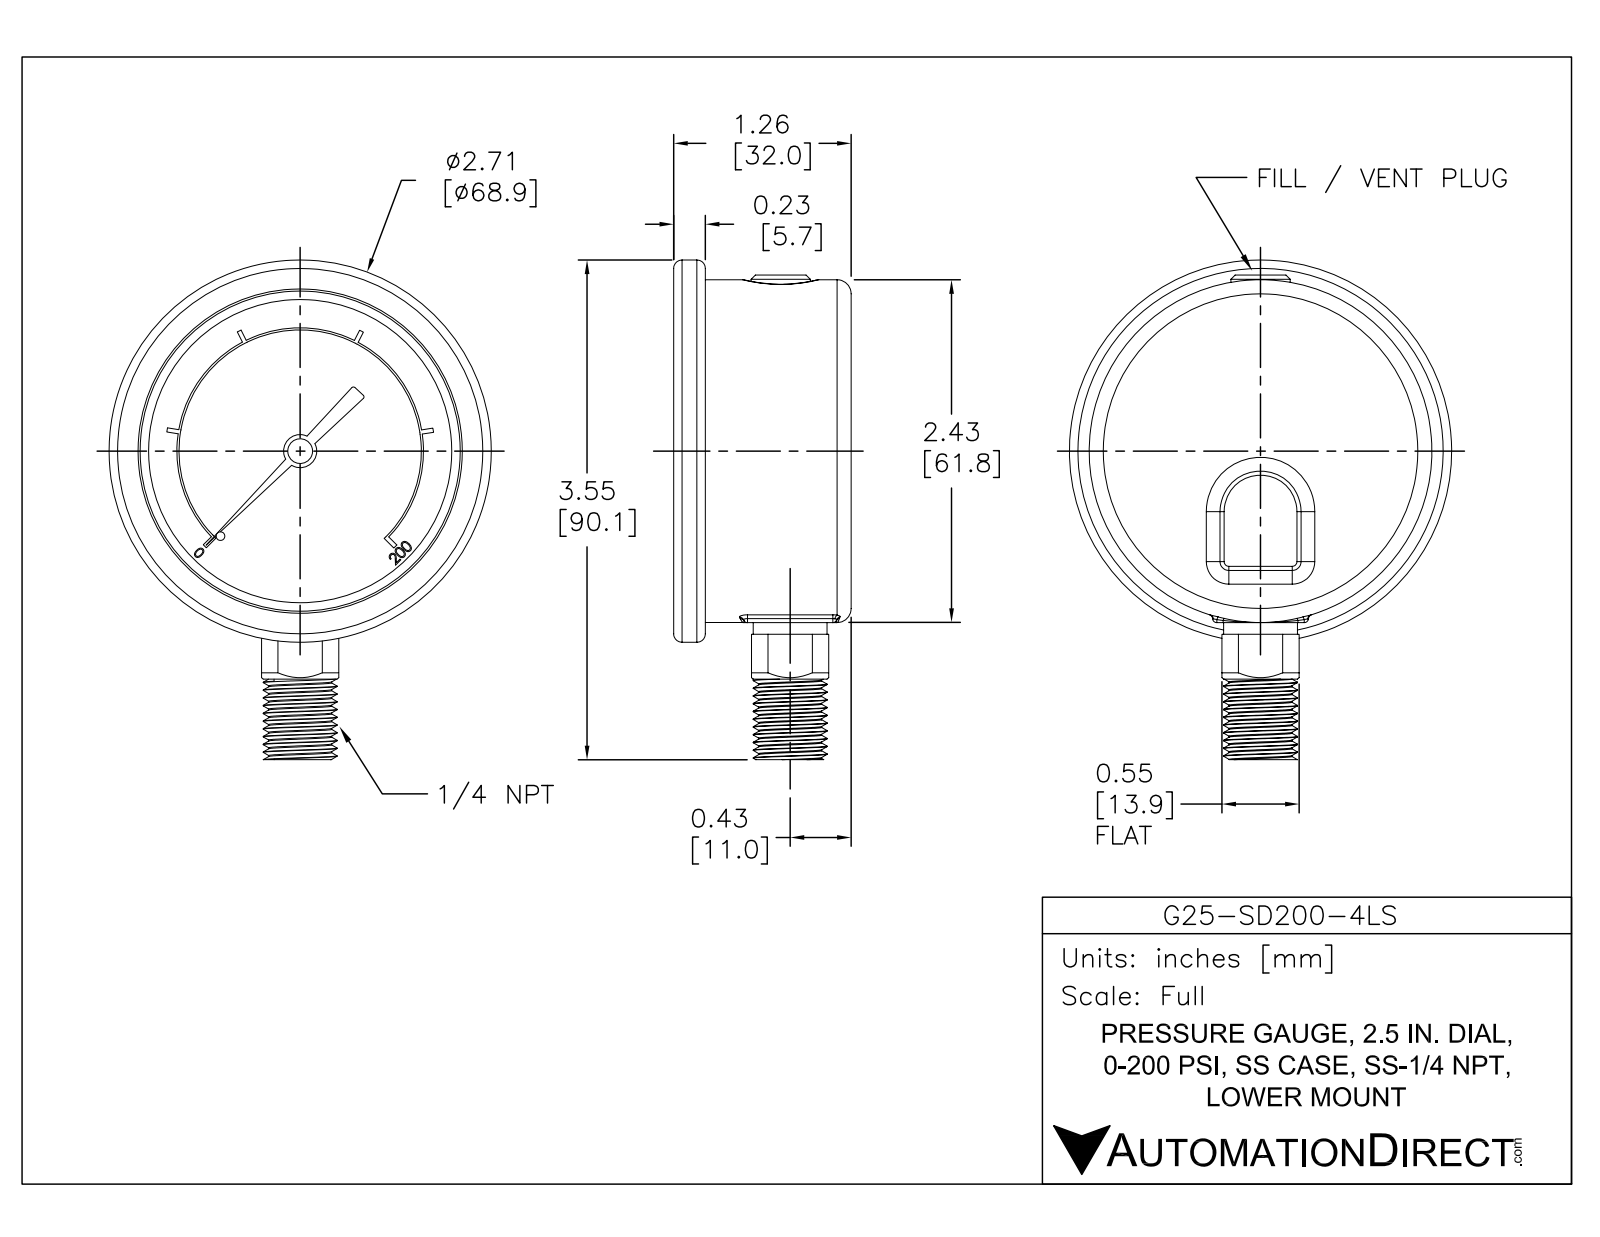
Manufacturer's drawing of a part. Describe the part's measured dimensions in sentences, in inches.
The part is named "G25-SD200-4LS". Its 3-D file was written by "SolidWorks 2021 (AUTOMOTIVE_DESIGN)". It is 1 solid with 349 faces: 195 planar, 85 cylindrical and 69 other. Overall it measures 3.546 by 2.713 by 1.26 inches. Its volume is 5.273 cubic inches and its surface area 24.68 square inches. Round holes: 1 of diameter 0.027, 1 of diameter 0.071, 1 of diameter 0.119, 1 of diameter 2.272. Round bosses or shafts: 1 of diameter 2.713, 1 of diameter 2.433, 1 of diameter 0.524, 1 of diameter 0.42, 1 of diameter 0.235, 1 of diameter 0.176, 1 of diameter 0.14, 1 of diameter 0.041. Partial cylindrical surfaces (rounded edges, fillets, slot ends): 9 of radius 0.03, 3 of radius 0.1, 2 of radius 0.015, 1 of radius 0.316, 1 of radius 0.86, 1 of radius 0.875. The main face-to-face distances are 1.01, 1.26, 0.25, 1.035, 0.025, 0.225, 0.1, 0.91, 0.935, 1.16. The hole center spacings are 0.067.
